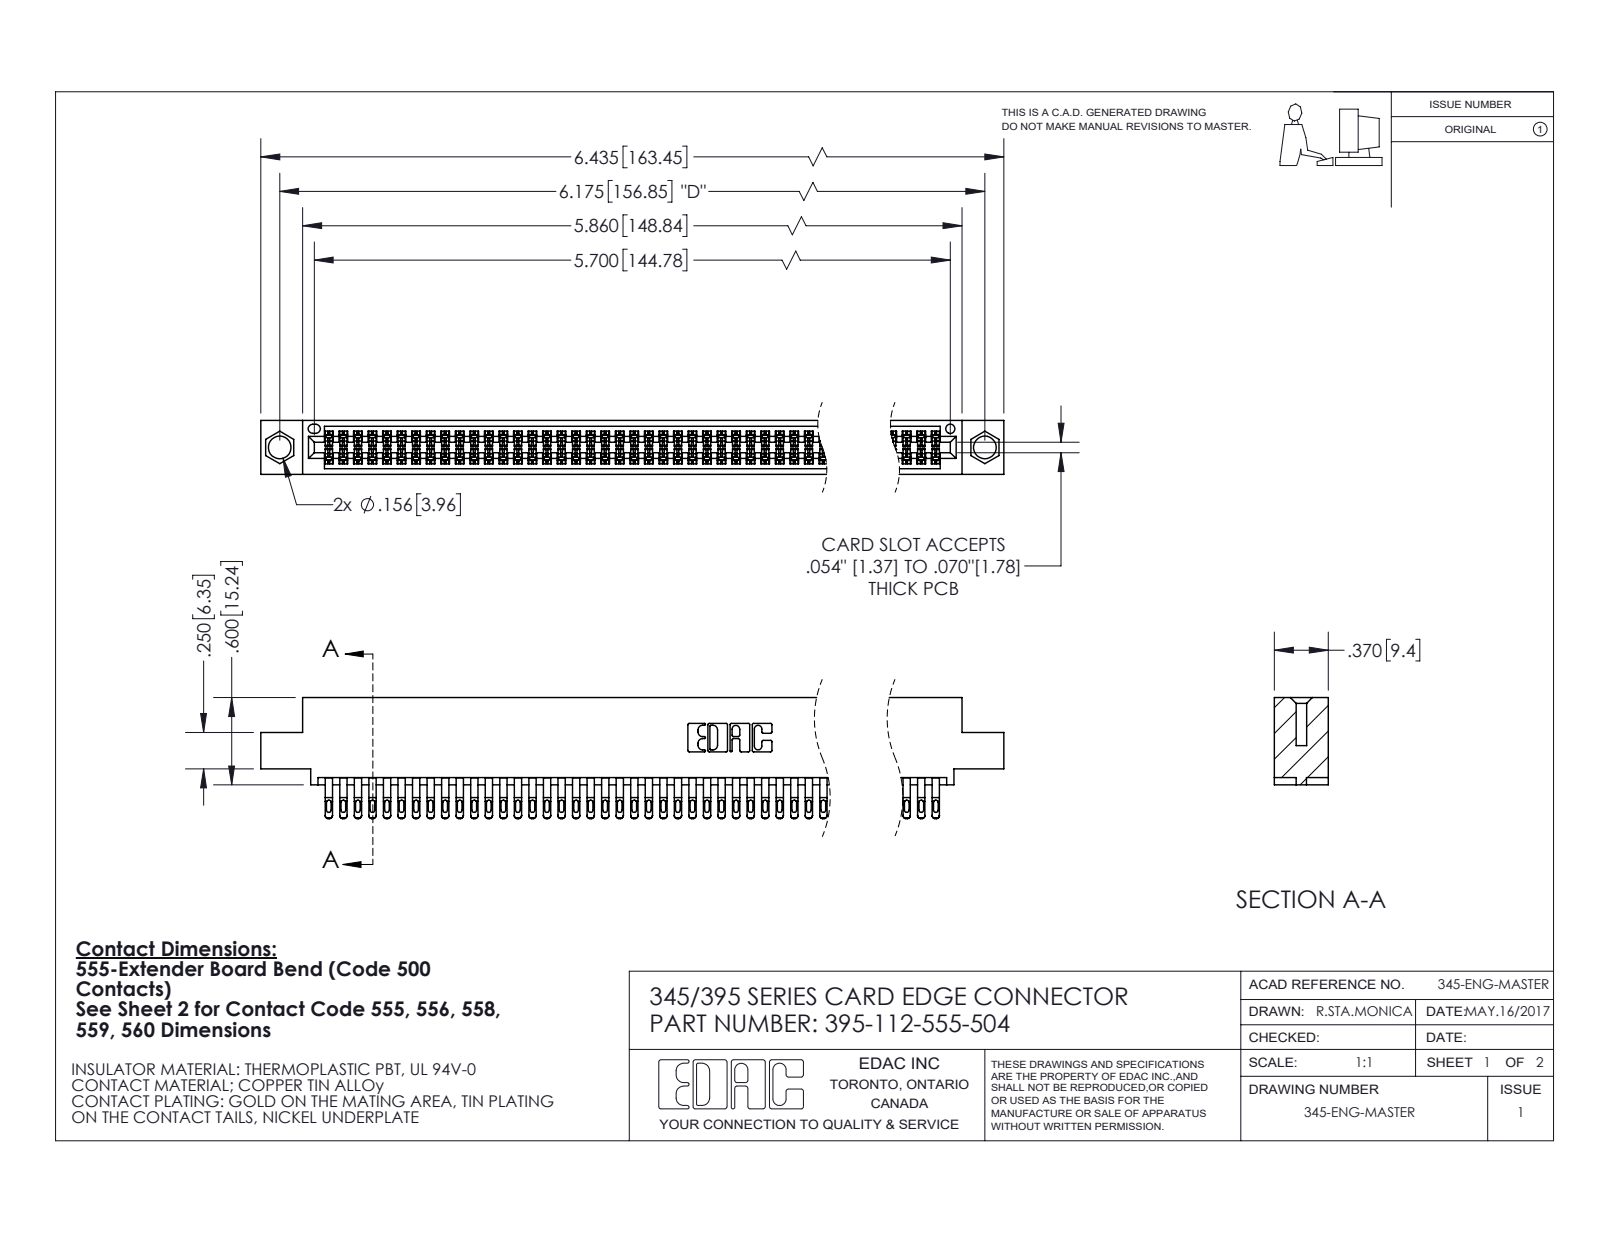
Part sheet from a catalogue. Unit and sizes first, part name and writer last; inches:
Units: inches
Overall size (bounding box): 6.435 × 0.832 × 0.37
Round holes (diameter × count): ⌀0.156 ×2, ⌀0.064 ×1
Partial cylindrical surfaces — rounded edges, fillets, slot ends (radius × count): R0.016 ×280, R0.006 ×224, R0.02 ×224, R0.01 ×22, R0.007 ×6, R0.031 ×6, R0.026 ×3, R0.01 ×2
Main face-to-face distances: 0.298, 0.072, 0.025, 0.37, 0.2, 0.098, 0.272, 0.225, 0.175, 0.149
Hole centre spacings: 0.27, 5.939, 6.175
Volume: 0.986 in³ · Surface area: 39.09 in²
Bodies: 113 solids, 6416 faces (3570 planar, 2846 cylindrical, 0 other)
Part name (STEP PRODUCT): 345-292-001_555 Tail; 345 Part_0.110 Offset - 0.156 Dia-TI; 395-112-555-504
STEP written by: SolidWorks 2020 (CONFIG_CONTROL_DESIGN)
